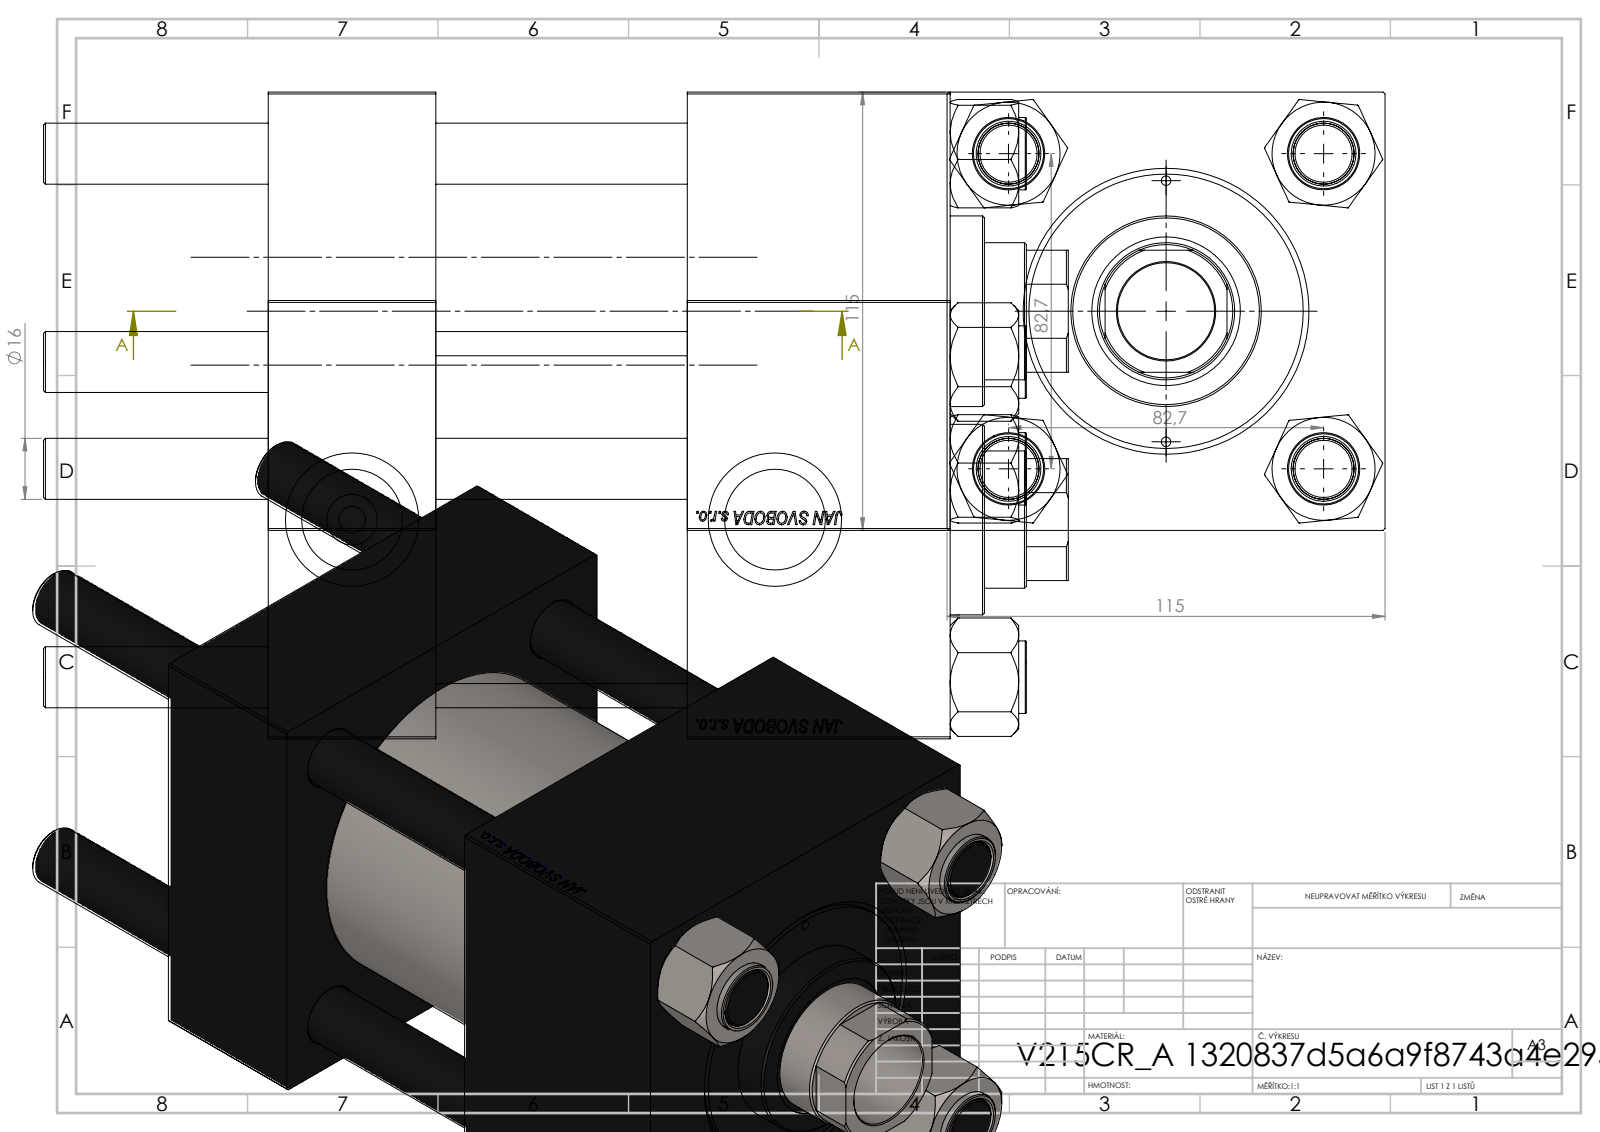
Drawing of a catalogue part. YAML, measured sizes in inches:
part_name: "V215_VC_A; CR025_012_A_0_G_A_G_M_020_+#_##_TYCINKA; V215CR_VCP; NUT_M5 (+1 more)"
step_written_by: "SolidWorks 2019 (CONFIG_CONTROL_DESIGN)"
units: inches
bodies: {solids: 11, faces: 1188, planar: 570, cylindrical: 82, other: 536}
overall_size: [10.591, 4.528, 4.528]
volume: 113.9
surface_area: 456.7
round_holes:
  - {diameter: 0.63, count: 4}
  - {diameter: 0.098, count: 2}
  - {diameter: 0.276, count: 2}
  - {diameter: 1.041, count: 2}
  - {diameter: 1.378, count: 2}
  - {diameter: 1.004, count: 1}
  - {diameter: 1.417, count: 1}
  - {diameter: 1.535, count: 1}
  - {diameter: 2.402, count: 1}
  - {diameter: 2.835, count: 1}
  - {diameter: 3.15, count: 1}
round_bosses_or_shafts:
  - {diameter: 0.748, count: 4}
  - {diameter: 3.386, count: 1}
  - {diameter: 1.969, count: 1}
partial_cylinders:
  - {radius: 0.689, count: 1}
face_to_face_distances: [4.528, 1.732, 7.047, 5.315, 4.331, 2.717, 2.598, 0.787, 3.504, 5.917]
hole_center_spacings: [1.652, 2.302, 3.256, 3.393, 1.348, 4.605, 2.697, 4.37]
